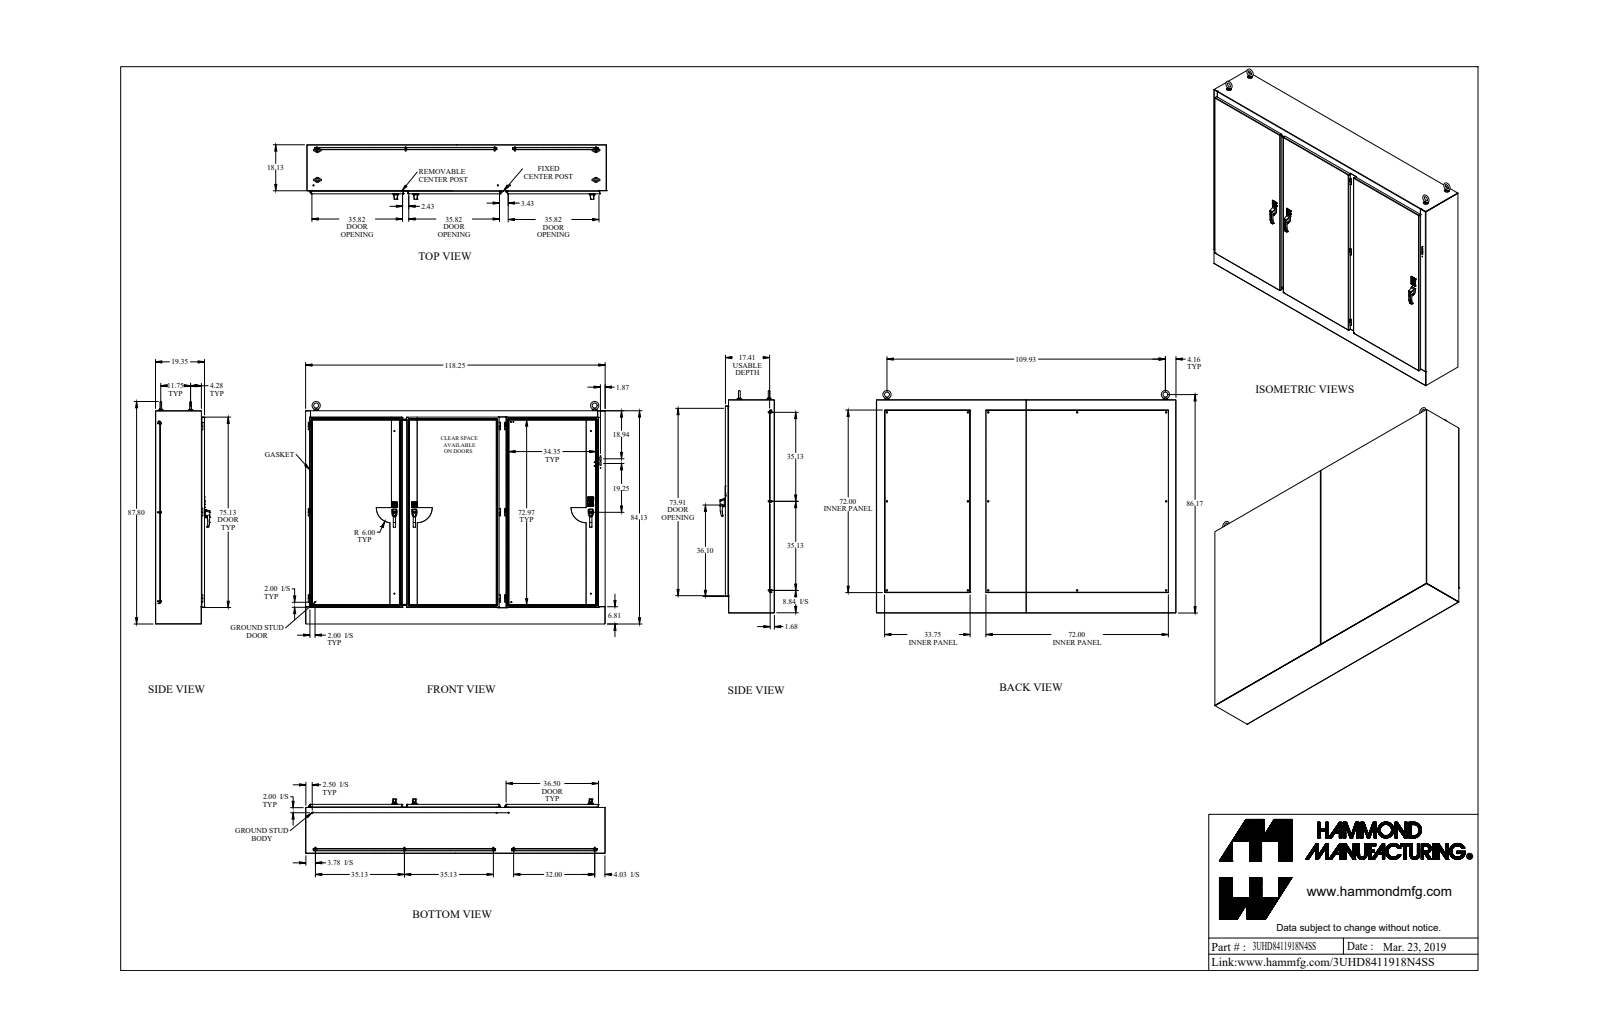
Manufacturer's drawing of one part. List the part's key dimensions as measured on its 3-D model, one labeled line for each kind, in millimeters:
Part name (STEP PRODUCT): 3UHD8411918N4SS
STEP written by: SolidWorks 2018 (AUTOMOTIVE_DESIGN)
Units: millimetres
Bodies: 310 solids, 4550 faces (2764 planar, 1295 cylindrical, 491 other)
Overall size (bounding box): 3003.6 × 2230.1 × 545.2
Volume: 61 980 000 mm³ · Surface area: 55 060 000 mm²
Round holes (diameter × count): ⌀6.4 ×23, ⌀5 ×20, ⌀7.8 ×14, ⌀7.1 ×10, ⌀8 ×9, ⌀8.9 ×9, ⌀11.3 ×9, ⌀22.2 ×8, ⌀4 ×6, ⌀6.8 ×6, ⌀9.9 ×6, ⌀6.5 ×5
Round bosses / shafts (diameter × count): ⌀25.4 ×21, ⌀6.4 ×17, ⌀9.5 ×15, ⌀16.5 ×14, ⌀8.4 ×14, ⌀6.2 ×10, ⌀15.9 ×7, ⌀12.3 ×7
Partial cylindrical surfaces — rounded edges, fillets, slot ends (radius × count): R3.2 ×70, R0.4 ×48, R1.5 ×44, R1.2 ×37, R3.6 ×37, R12.7 ×36, R6.4 ×32, R4.7 ×20
Main face-to-face distances: 2.4, 2, 443.5, 491.9, 489.5, 489.9, 487.5, 48.4, 46, 441.5
Hole centre spacings: 892.2, 1784.4, 1968.5, 54, 199.9, 298.5, 892.2, 1768.6
